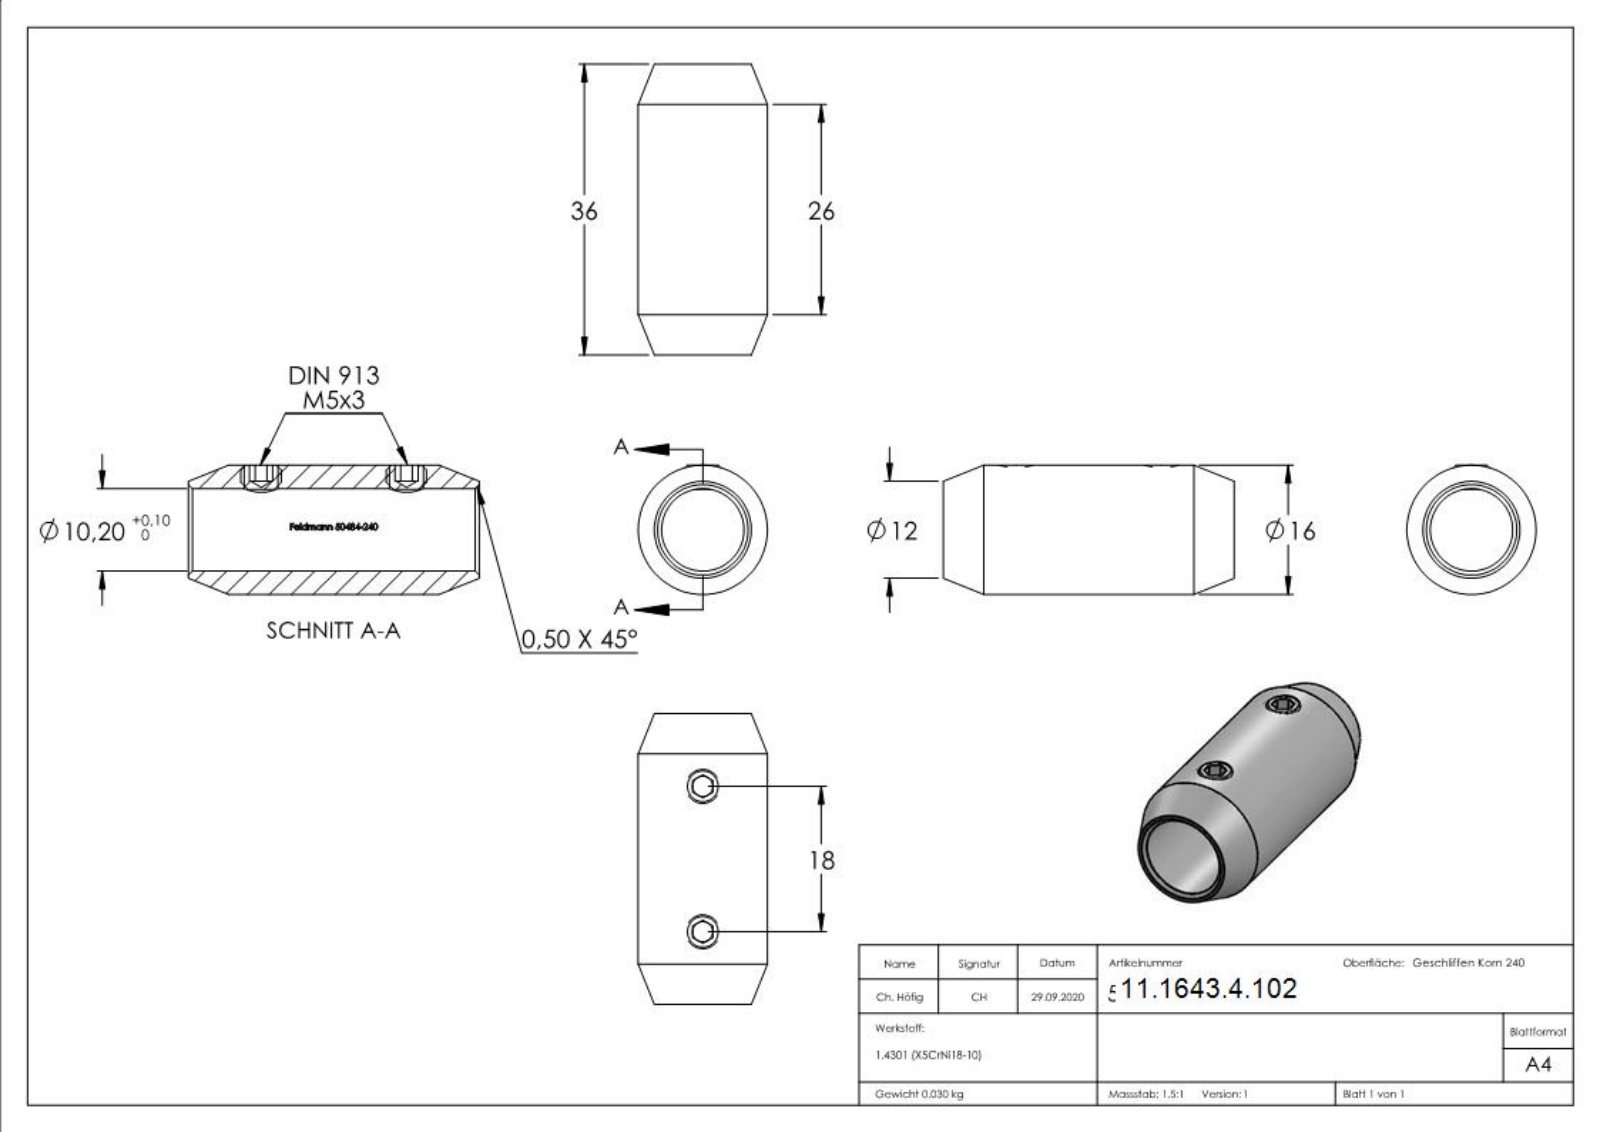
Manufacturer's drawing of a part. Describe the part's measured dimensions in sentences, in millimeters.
The part is named "DIN913; 5048X-240 Teil1; 50484-240; 5048X-240 Teil1_50484-240 Teil1 (+1 more)". Its 3-D file was written by "SolidWorks 2018 (CONFIG_CONTROL_DESIGN)". It is 3 solids with 301 faces: 139 planar, 45 cylindrical and 117 other. Overall it measures 70000 by 5000 by 5000 millimeters. Its volume is 3 823 cubic millimeters and its surface area 3 186 square millimeters. Round holes: 2 of diameter 4.2, 1 of diameter 10.2. Round bosses or shafts: 2 of diameter 5, 1 of diameter 16. Partial cylindrical surfaces (rounded edges, fillets, slot ends): 1 of radius 5.2. The main face-to-face distances are 2.5, 36, 3, 15.58, 18.08, 13.08, 1, 2, 4.65, 5.21. The hole center spacings are 18.
